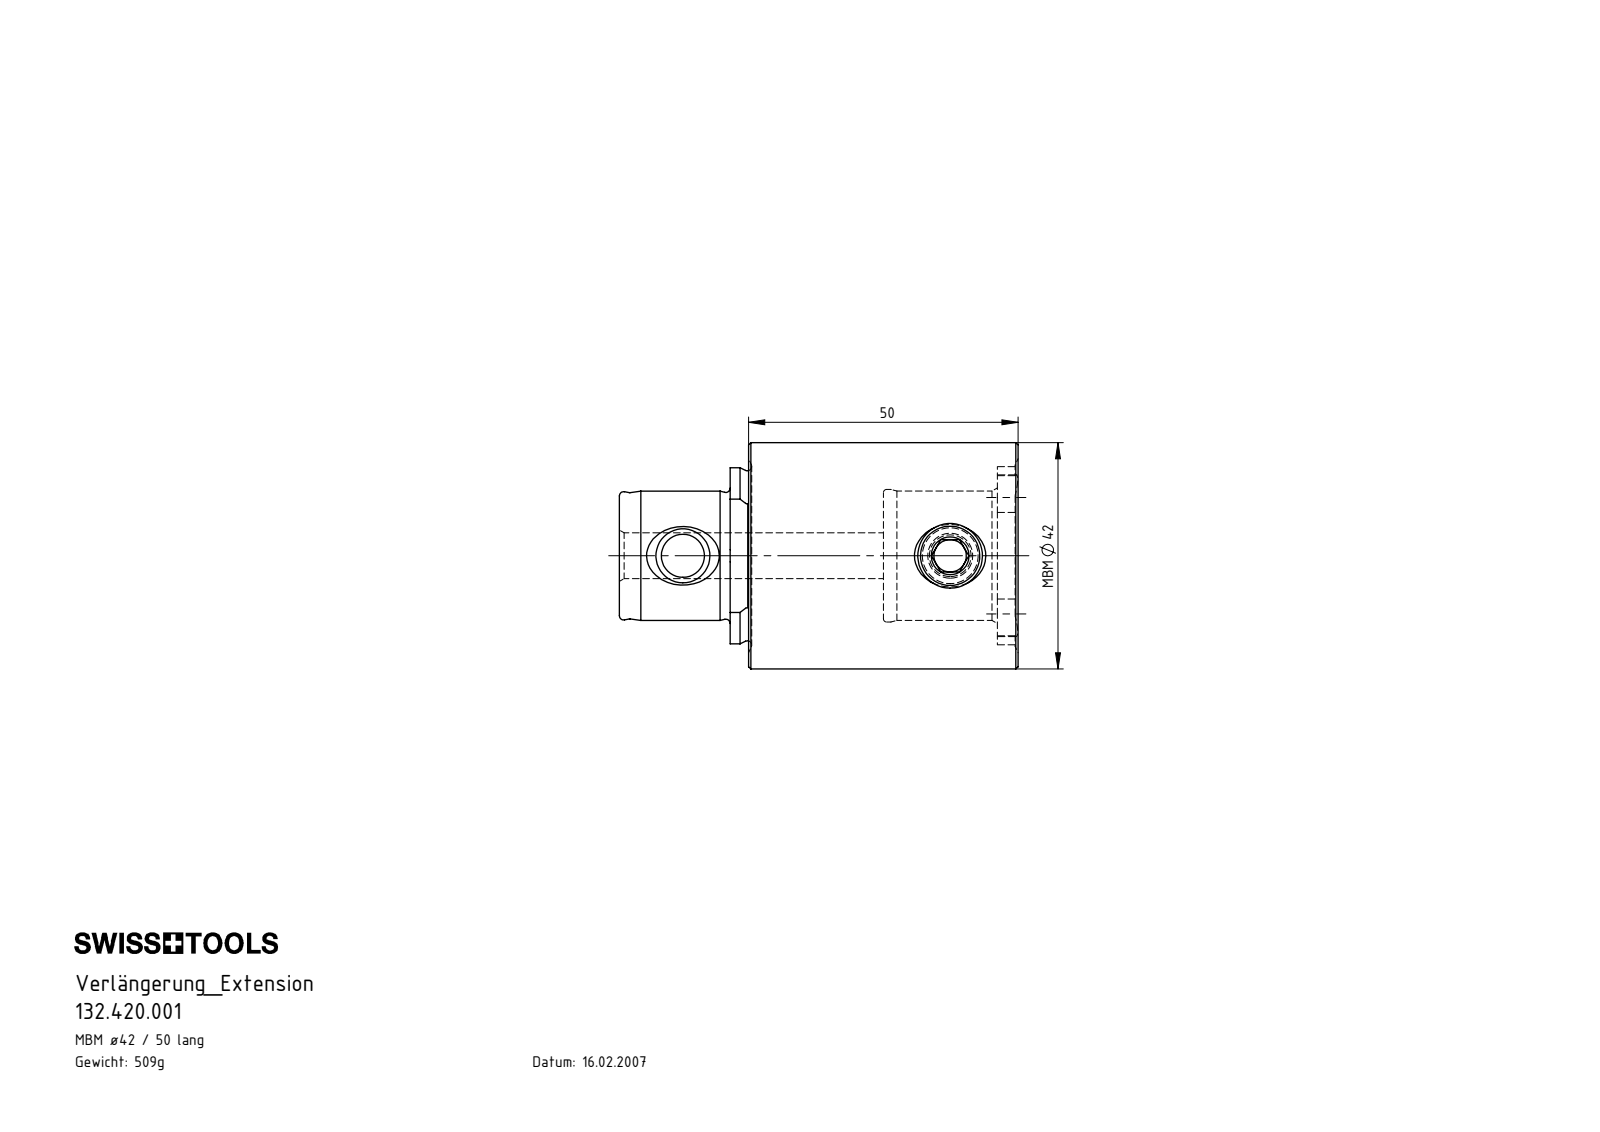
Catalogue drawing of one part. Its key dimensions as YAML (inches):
part_name: "MB4-ER1.001.013_A; MB4-MB4.K01.050_B; MB4.MB4.K01.050"
step_written_by: "SolidWorks 2012 (CONFIG_CONTROL_DESIGN)"
units: inches
bodies: {solids: 2, faces: 118, planar: 29, cylindrical: 30, other: 59}
overall_size: [2.913, 1.654, 1.654]
volume: 3.957
surface_area: 23.72
round_holes:
  - {diameter: 0.315, count: 1}
  - {diameter: 0.335, count: 1}
  - {diameter: 0.433, count: 1}
  - {diameter: 0.945, count: 1}
  - {diameter: 0.969, count: 1}
round_bosses_or_shafts:
  - {diameter: 1.654, count: 1}
  - {diameter: 0.472, count: 1}
partial_cylinders:
  - {radius: 0.165, count: 4}
  - {radius: 0.587, count: 1}
  - {radius: 0.643, count: 1}
  - {radius: 0.65, count: 1}
face_to_face_distances: [0.984, 1.969, 1.817, 0.833, 0.152, 1.953, 0.945, 1.929, 2.762, 2.913]
hole_center_spacings: [1.955]
